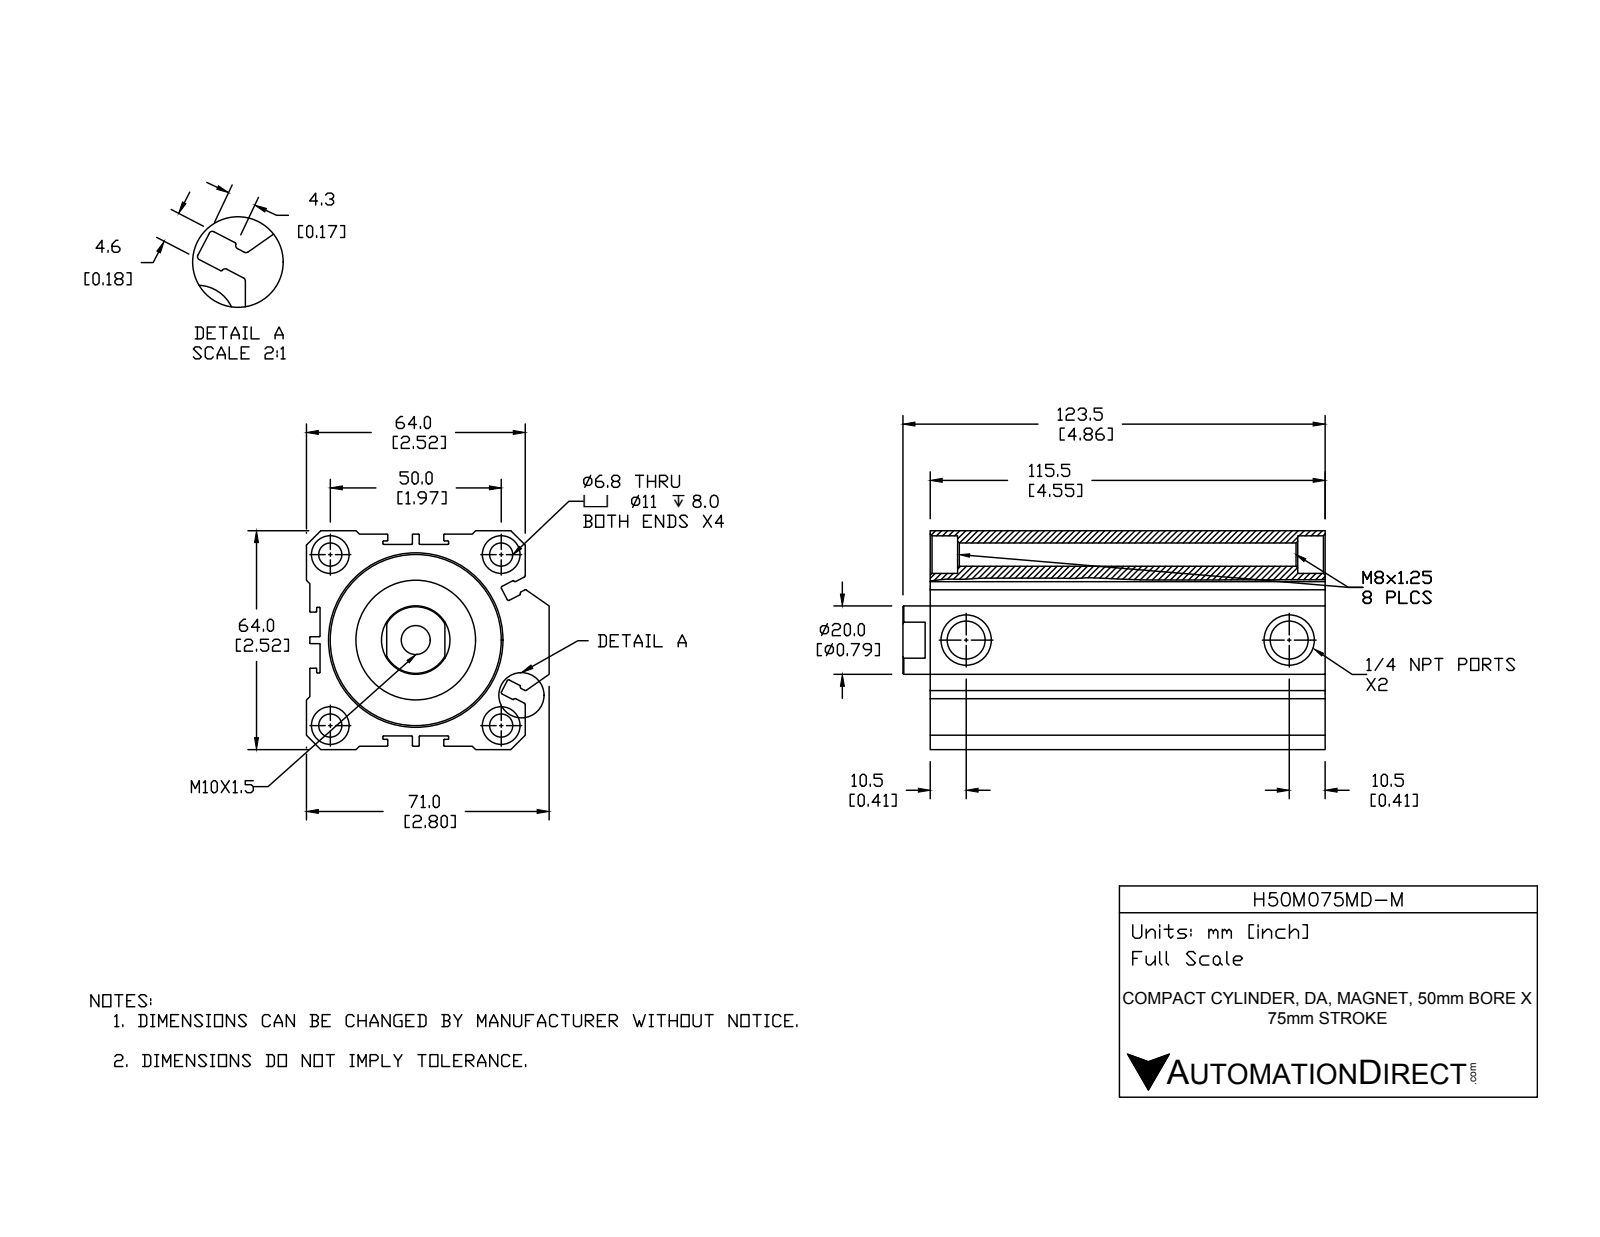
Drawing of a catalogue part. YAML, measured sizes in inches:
part_name: "H50M075MD-M-PISTON; H50M075MD-M; H50M075MD-M-BODY"
step_written_by: "SolidWorks 2015 (CONFIG_CONTROL_DESIGN)"
units: inches
bodies: {solids: 2, faces: 255, planar: 99, cylindrical: 103, other: 53}
overall_size: [4.862, 2.795, 2.52]
volume: 18.13
surface_area: 142.7
round_holes:
  - {diameter: 0.268, count: 4}
  - {diameter: 0.433, count: 4}
  - {diameter: 0.438, count: 2}
  - {diameter: 0.335, count: 1}
  - {diameter: 0.787, count: 1}
  - {diameter: 1.417, count: 1}
  - {diameter: 1.969, count: 1}
round_bosses_or_shafts:
  - {diameter: 1.378, count: 1}
  - {diameter: 1.22, count: 1}
partial_cylinders:
  - {radius: 0.008, count: 40}
  - {radius: 0.02, count: 12}
face_to_face_distances: [0.157, 0.039, 0.118, 2.48, 2.362, 2.52, 2.323, 0.276, 1.181, 0.079]
hole_center_spacings: [1.392, 1.969, 2.784, 3.72]
